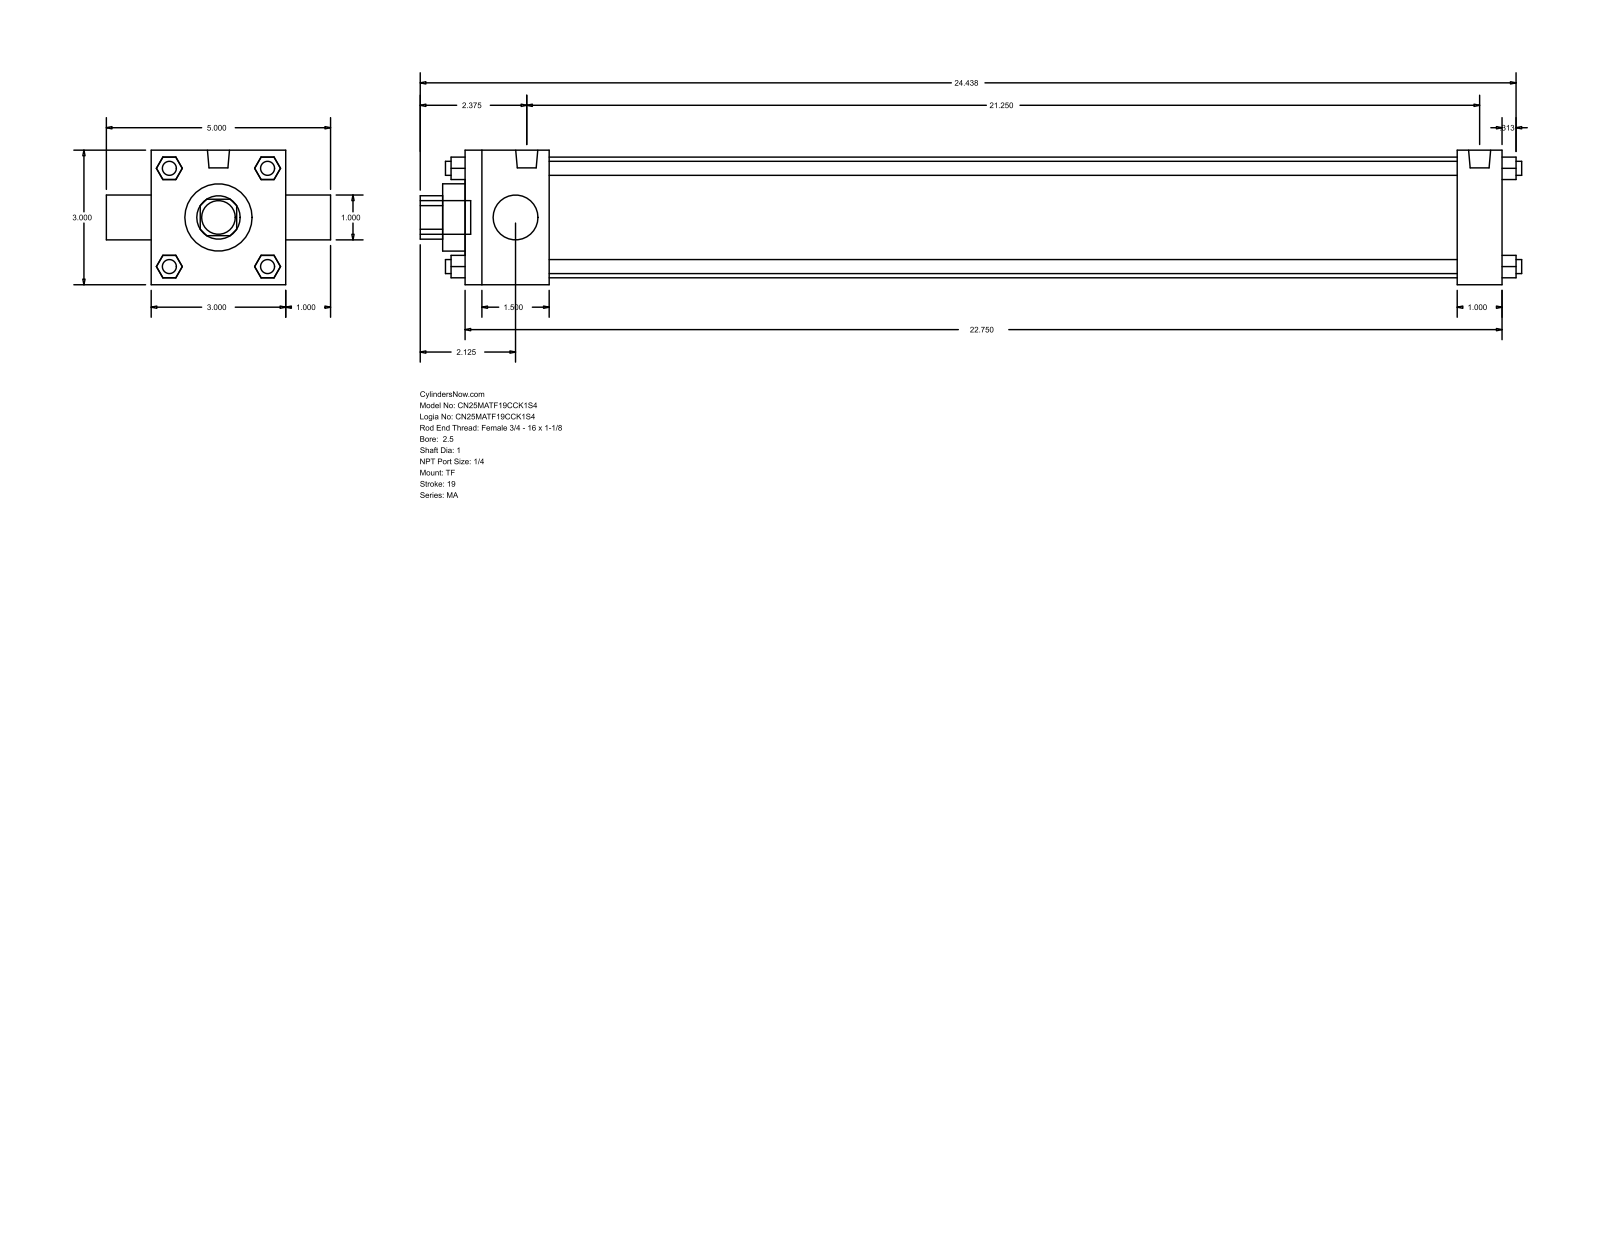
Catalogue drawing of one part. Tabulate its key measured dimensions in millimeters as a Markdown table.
| quantity | value |
| --- | --- |
| part name | MA_TF__0250_1 |
| STEP written by | GSSL Pune (CONFIG_CONTROL_DESIGN) |
| units | millimeters |
| bodies | 0 solids, 120 faces (92 planar, 28 cylindrical, 0 other) |
| overall size | 623.89 × 127 × 76.2 |
| round holes (diameter × count) | 25.4 × 2, 38.1 × 1, 68.33 × 1 |
| round bosses / shafts (diameter × count) | 7.94 × 7, 12.49 × 2, 19.05 × 1 |
| partial cylindrical surfaces (radius × count) | 12.29 × 1 |
| main face-to-face distances | 76.2, 587.37, 12.7, 47.63, 561.98, 514.35, 539.74, 25.39, 25.4, 101.6 |
